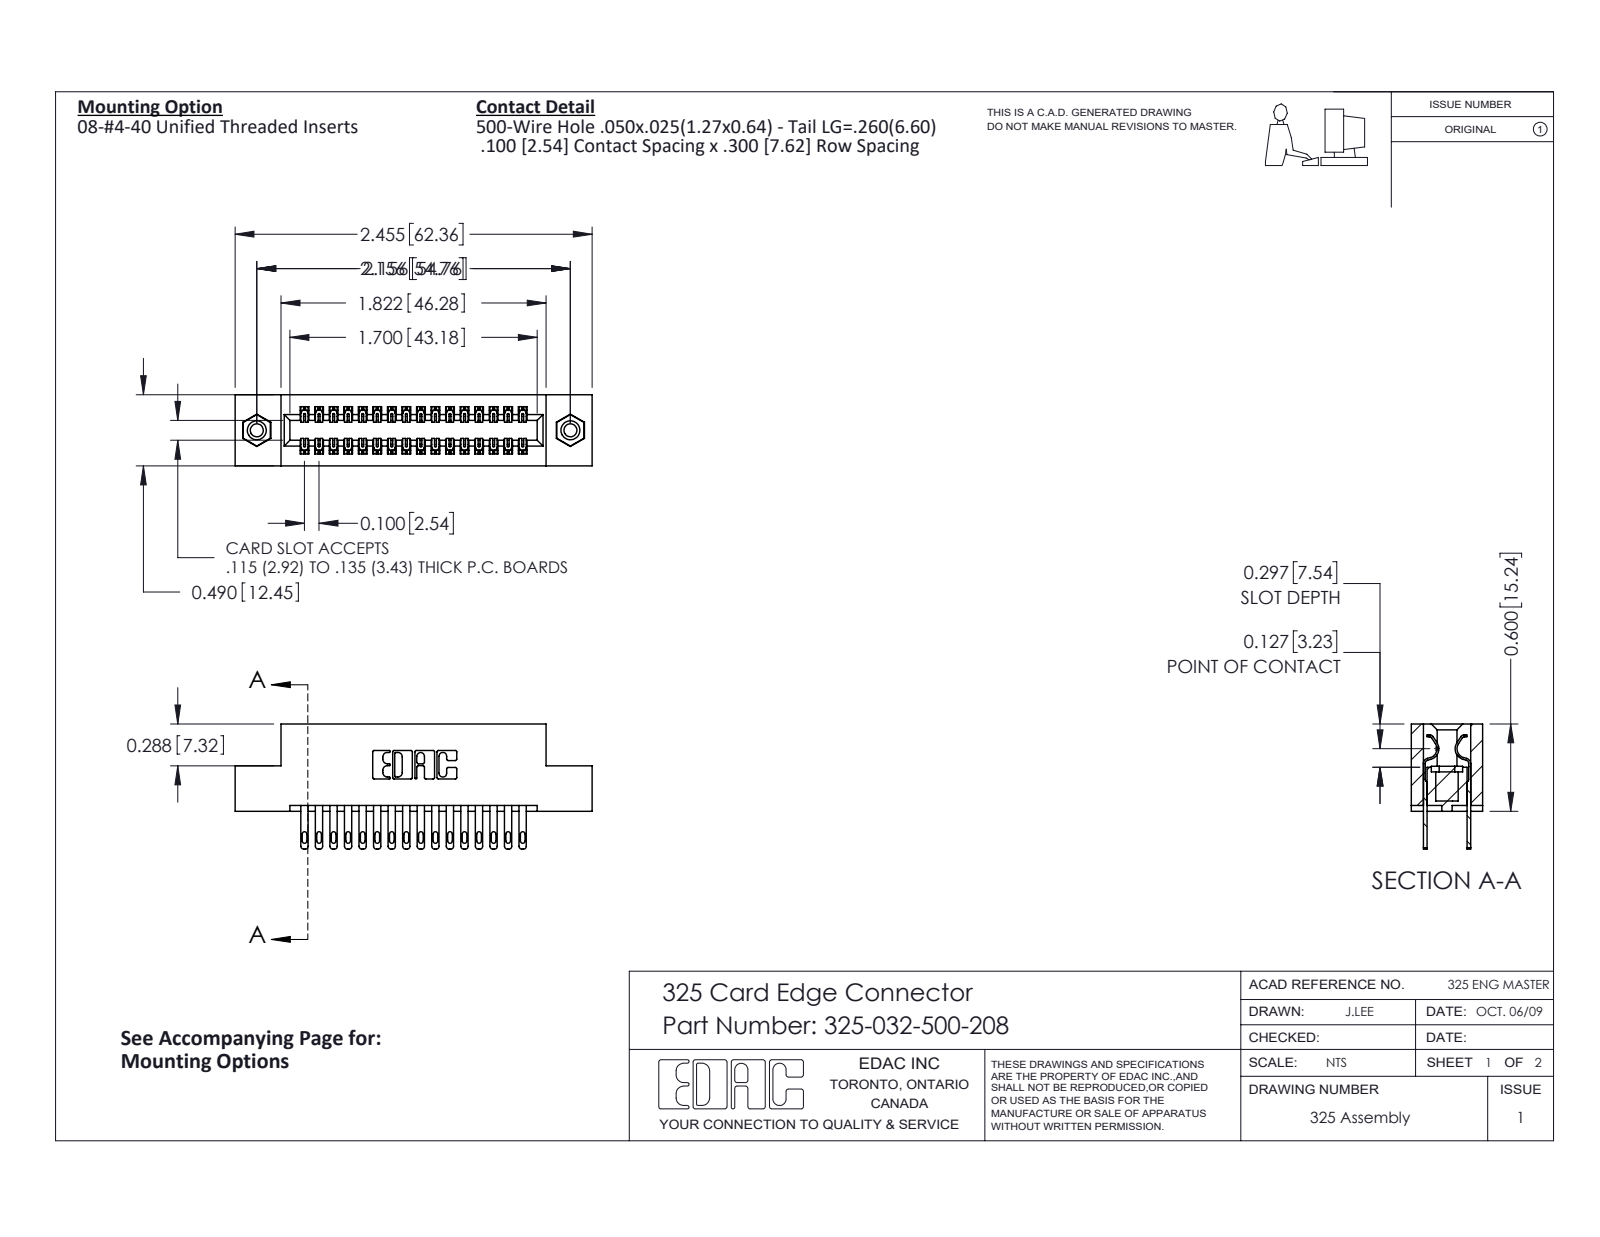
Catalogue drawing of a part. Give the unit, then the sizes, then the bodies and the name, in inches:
Units: inches
Overall size (bounding box): 2.455 × 0.86 × 0.49
Round holes (diameter × count): ⌀0.089 ×2, ⌀0.125 ×2, ⌀0.16 ×2
Round bosses / shafts (diameter × count): ⌀0.155 ×2
Partial cylindrical surfaces — rounded edges, fillets, slot ends (radius × count): R0.006 ×48, R0.016 ×32, R0.02 ×32, R0.01 ×22, R0.007 ×6, R0.031 ×6, R0.026 ×3, R0.014 ×2
Main face-to-face distances: 0.083, 0.407, 0.3, 0.107, 0.383, 0.025, 0.49, 0.325, 0.04, 0.1
Hole centre spacings: 2.156
Volume: 0.483 in³ · Surface area: 14.42 in²
Bodies: 35 solids, 1710 faces (1062 planar, 632 cylindrical, 16 other)
Part name (STEP PRODUCT): 325 Part_TI; 325-032-500-208; 345-250-001_345-250-003-102; 325-292-001_325-293-100
STEP written by: SolidWorks 2016 (CONFIG_CONTROL_DESIGN)
